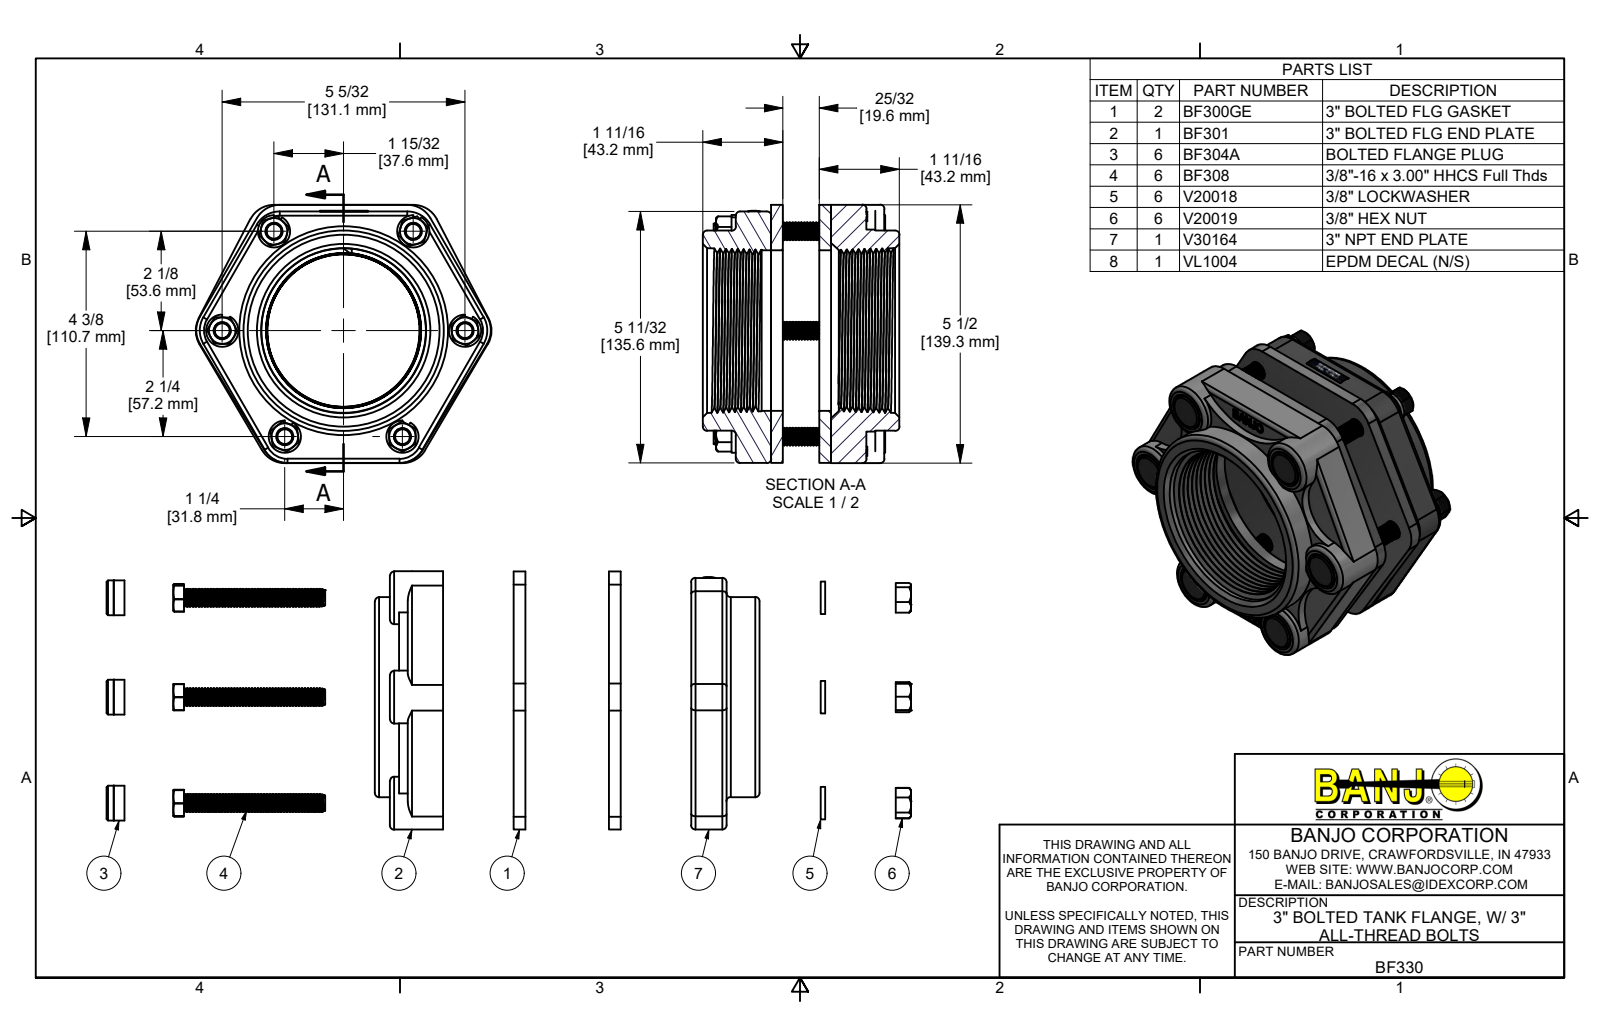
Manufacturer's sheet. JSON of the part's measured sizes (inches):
{"part_name": "BF330; BF301; BF300GE; V30164 (+5 more)", "step_written_by": "Autodesk Inventor 2019 (AUTOMOTIVE_DESIGN)", "units": "inches", "bodies": {"solids": 29, "faces": 2251, "planar": 448, "cylindrical": 853, "other": 950}, "overall_size": [6.285, 5.485, 4.173], "volume_in3": 44.14, "surface_area_in2": 322.8, "round_holes": [[0.307, 6], [0.385, 6], [0.406, 6], [0.406, 6], [0.41, 6], [0.715, 6], [0.75, 6], [3.41, 1]], "round_bosses_or_shafts": [[0.324, 282], [1.125, 6], [0.742, 6], [0.687, 6], [0.375, 6], [4.25, 1]], "partial_cylinders_radius": [[0.09, 18], [0.162, 12], [0.322, 6], [0.56, 6], [0.562, 6], [0.794, 2], [1.094, 2], [0.517, 1]], "face_to_face_distances": [0.25, 1.023, 1.273, 0.773, 0.75, 1, 1.773, 2.023, 0.7, 1.45], "hole_center_spacings": [2.38, 2.574, 2.577, 2.58, 2.614, 4.366, 4.442, 4.575]}
